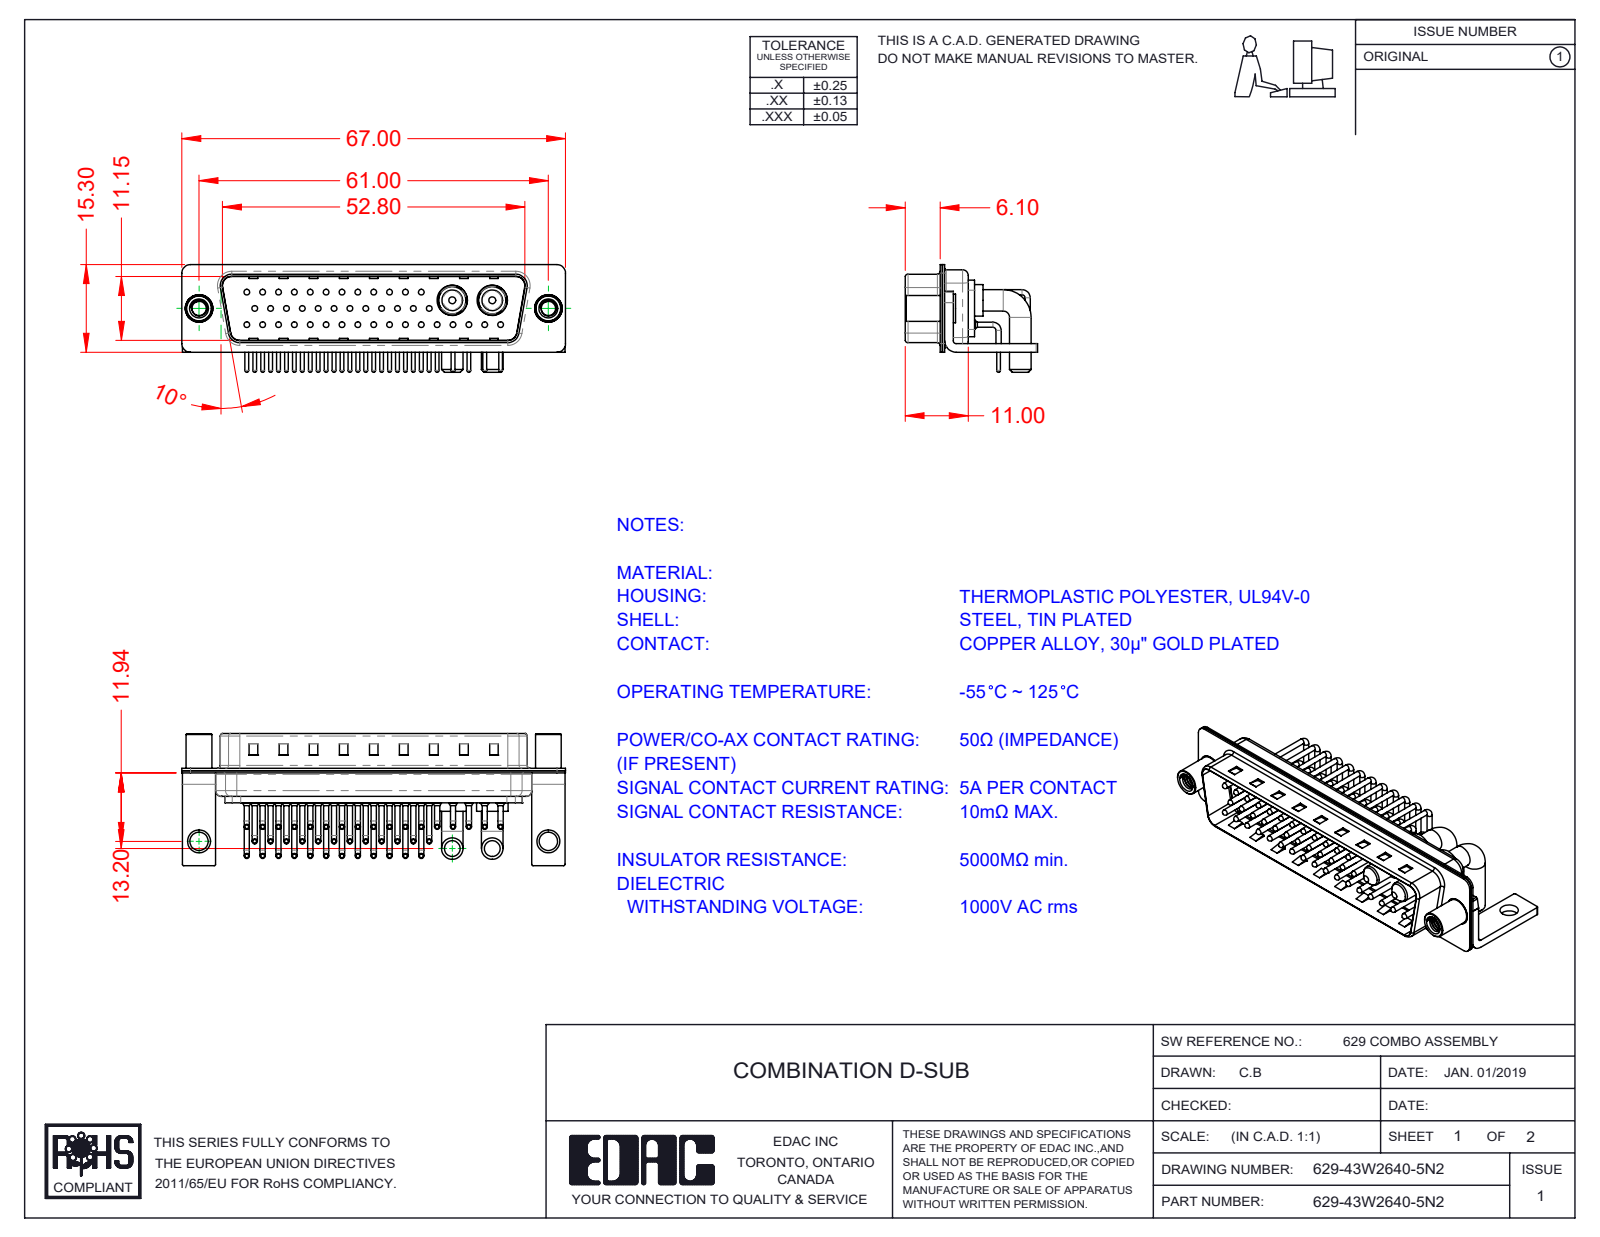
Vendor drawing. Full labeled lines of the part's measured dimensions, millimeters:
Part name (STEP PRODUCT): 629Combo Contact Row 3; Power Pin_40A RA 50; 629-43W2640-5N2; 629Combo Shell Front_50 Contacts (+6 more)
STEP written by: SolidWorks 2020 (CONFIG_CONTROL_DESIGN)
Units: millimetres
Bodies: 52 solids, 5106 faces (2869 planar, 1731 cylindrical, 506 other)
Overall size (bounding box): 67 × 23.1 × 18.8
Volume: 5 837 mm³ · Surface area: 13 730 mm²
Round holes (diameter × count): ⌀0.75 ×41, ⌀1.6 ×41, ⌀2 ×41, ⌀2.5 ×2, ⌀3.2 ×2, ⌀4 ×2, ⌀4.8 ×2, ⌀4.85 ×2, ⌀5.3 ×2
Round bosses / shafts (diameter × count): ⌀0.9 ×82, ⌀1.5 ×41, ⌀1 ×41, ⌀0.65 ×41, ⌀3.75 ×4, ⌀5.5 ×2, ⌀5.2 ×2, ⌀5 ×2
Partial cylindrical surfaces — rounded edges, fillets, slot ends (radius × count): R1.01 ×41, R0.25 ×16, R1.5 ×16, R2 ×13, R0.5 ×9, R1.6 ×8, R0.6 ×4, R0.65 ×4
Main face-to-face distances: 0.4, 1.5, 11.55, 5.6, 5.2, 0.8, 1.9, 4.1, 6, 0.78
Hole centre spacings: 2.77, 5.54, 3.16, 8.31, 11.08, 13.85, 16.62, 19.39
